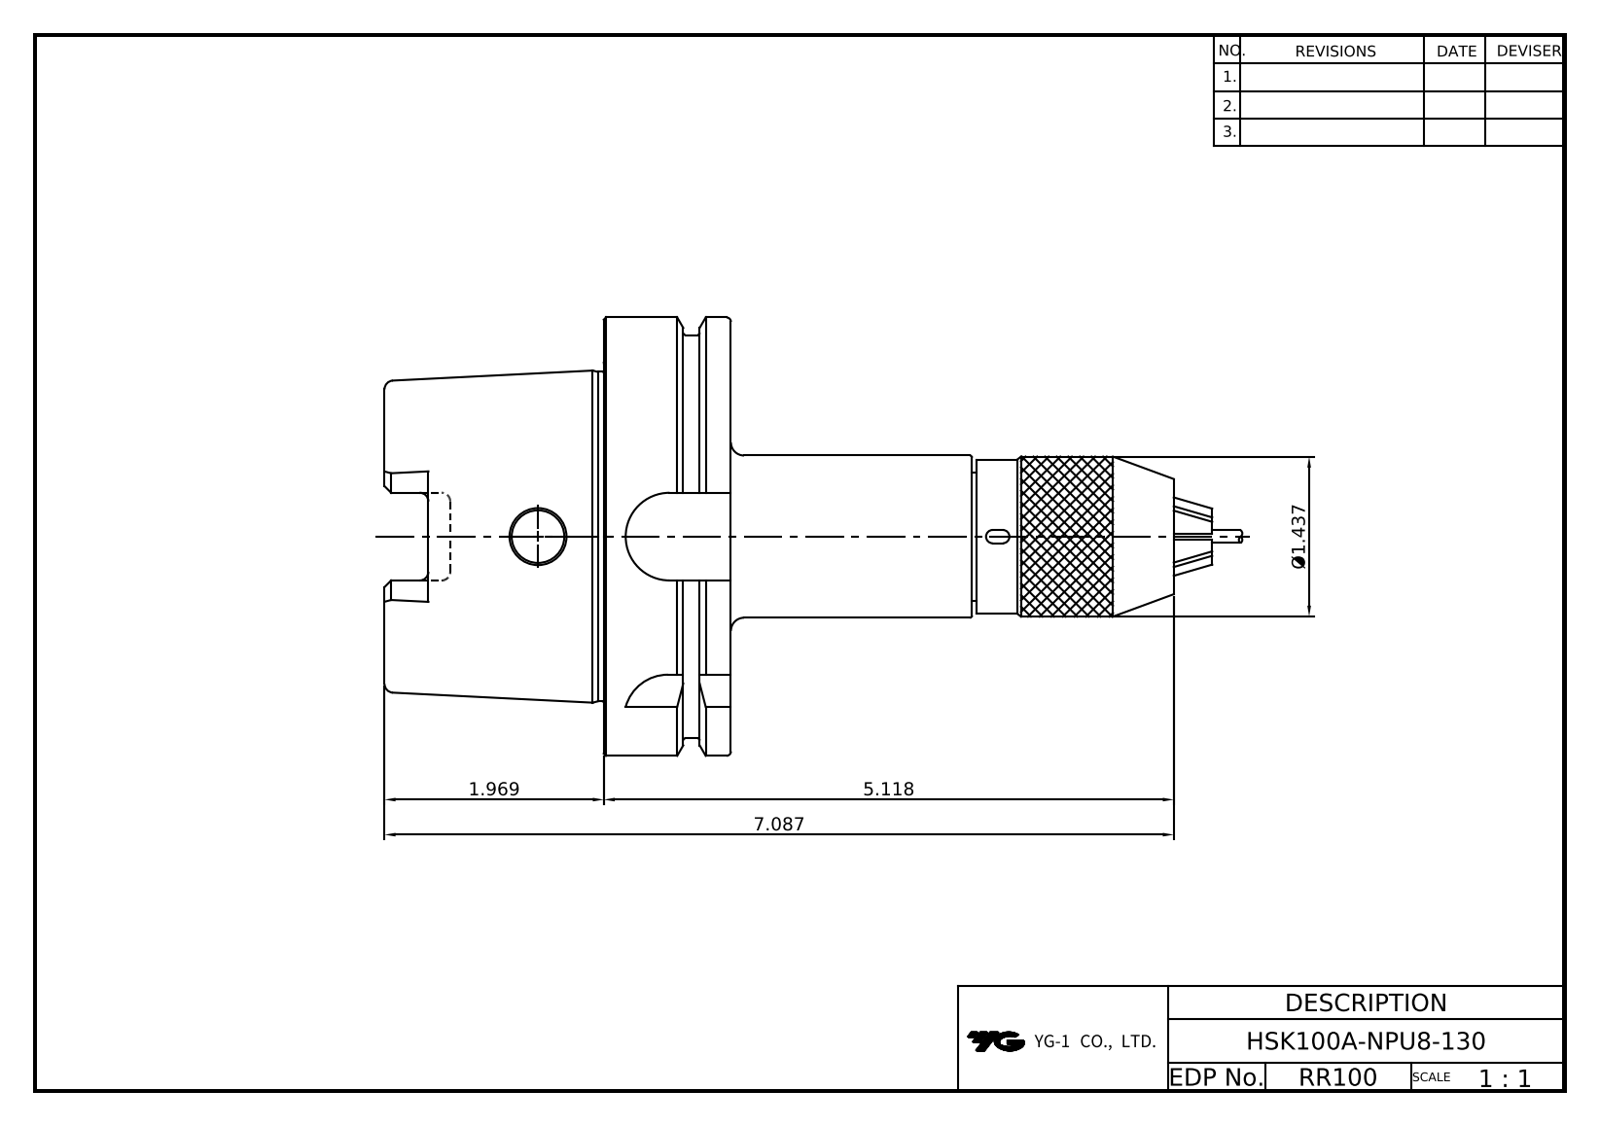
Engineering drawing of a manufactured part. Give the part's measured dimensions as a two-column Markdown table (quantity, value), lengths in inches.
| quantity | value |
| --- | --- |
| part name | LO-HSK100A-NPU8-130; NPU8; 12201-10305F; 12701-106C (+2 more) |
| STEP written by | Autodesk Inventor 2025 (AP242_MANAGED_MODEL_BASED_3D_ENGINEERING_MIM_LF) |
| units | inches |
| bodies | 7 solids, 228 faces (122 planar, 50 cylindrical, 56 other) |
| overall size | 7.367 × 3.937 × 3.937 |
| volume | 21.62 in³ |
| surface area | 111.8 in² |
| round holes (diameter × count) | 0.197 × 3, 0.472 × 2, 0.276 × 1, 0.394 × 1, 0.689 × 1, 0.881 × 1, 0.984 × 1, 1.201 × 1, 1.252 × 1, 2.087 × 1, 2.48 × 1 |
| round bosses / shafts (diameter × count) | 3.937 × 1, 3.622 × 1, 2.969 × 1, 1.476 × 1, 1.457 × 1, 1.417 × 1, 1.213 × 1, 1.181 × 1 |
| partial cylindrical surfaces (radius × count) | 0.079 × 6, 0.192 × 4, 0.394 × 4, 0.031 × 3, 0.217 × 3 |
| main face-to-face distances | 1.142, 2.52, 0.492, 3.661, 0.65, 3.169, 1.969, 1.594, 2.461, 2.736 |
